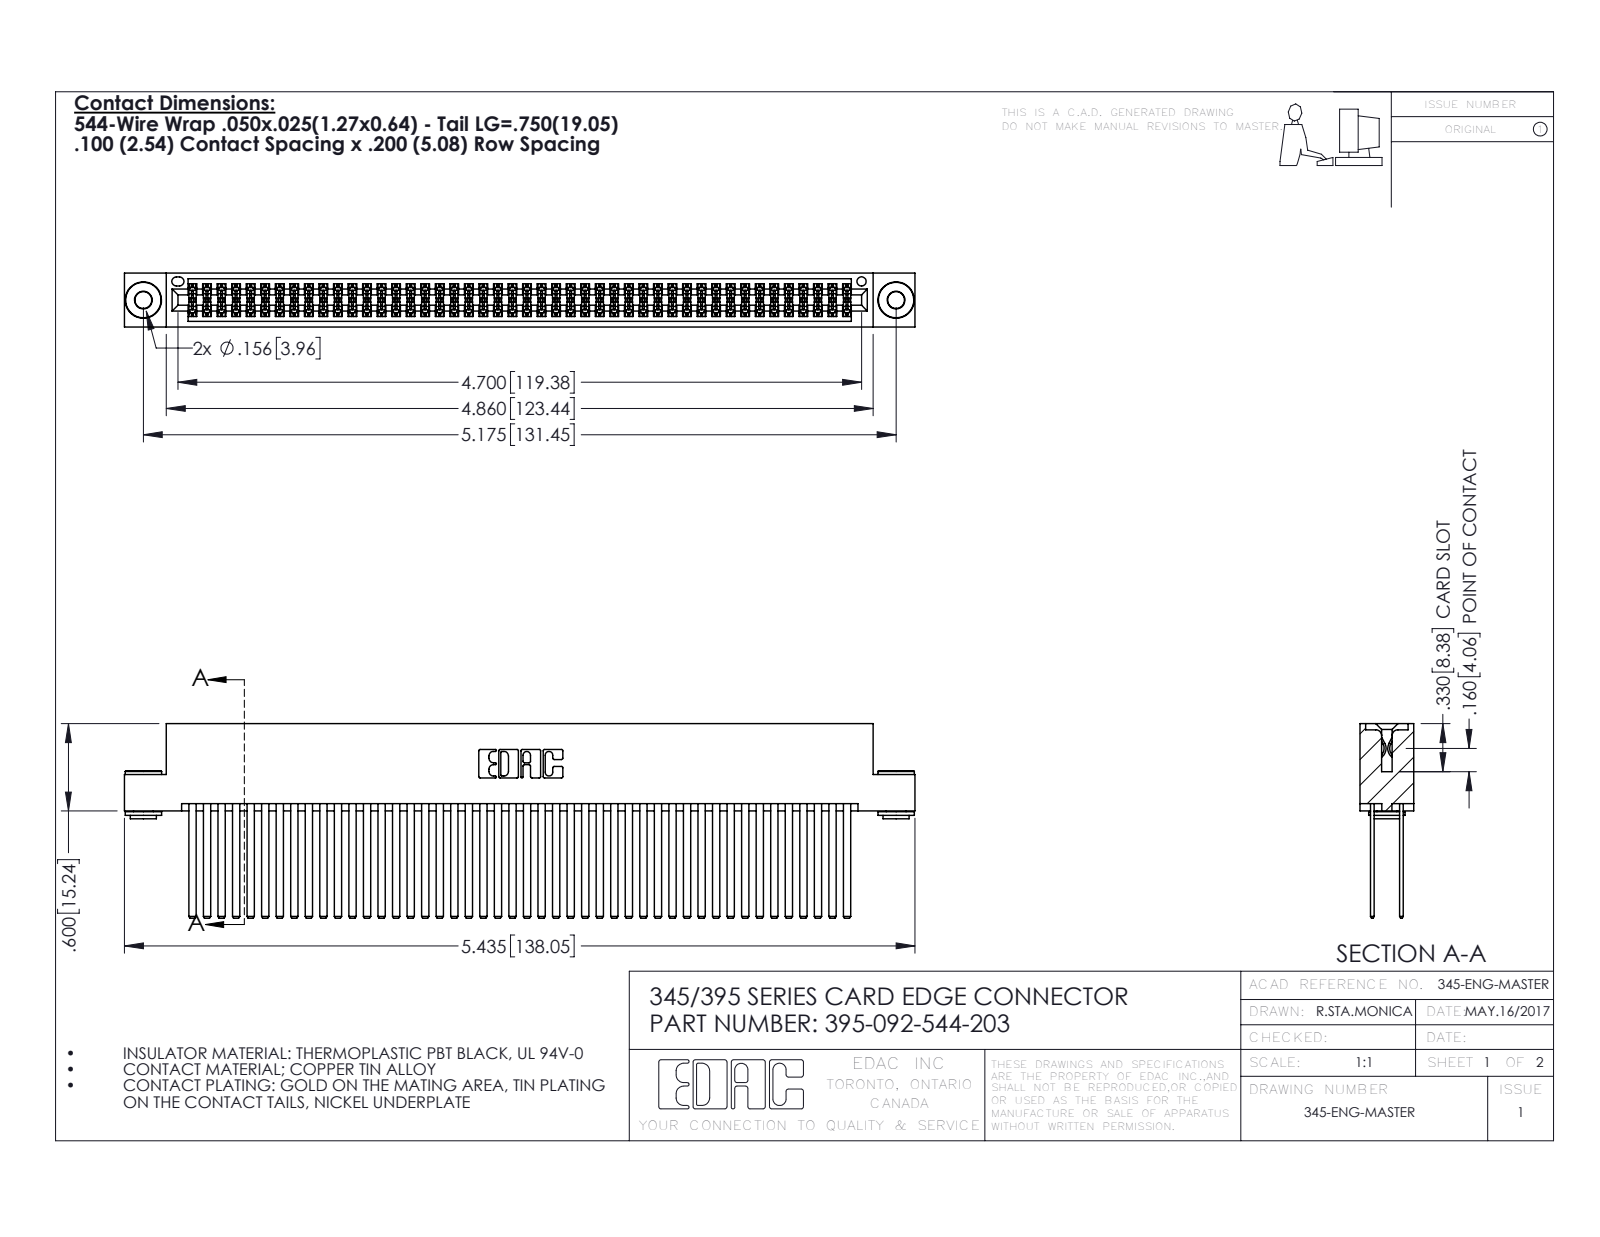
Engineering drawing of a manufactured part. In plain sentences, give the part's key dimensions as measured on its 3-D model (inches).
The part is named "345-292-001_345-293-144; 345 Part_Flush Mounting Lugs - 0.156 Dia-TH; 345-250-002_345-250-002-102; 395-092-544-203". Its 3-D file was written by "SolidWorks 2016 (CONFIG_CONTROL_DESIGN)". It is 95 solids with 4212 faces: 2758 planar, 1446 cylindrical and 8 other. Overall it measures 5.435 by 1.337 by 0.37 inches. Its volume is 0.9 cubic inches and its surface area 40.11 square inches. Round holes: 2 of diameter 0.116, 2 of diameter 0.156, 1 of diameter 0.064. Round bosses or shafts: 2 of diameter 0.25, 2 of diameter 0.18, 2 of diameter 0.136. Partial cylindrical surfaces (rounded edges, fillets, slot ends): 138 of radius 0.006, 22 of radius 0.01, 6 of radius 0.007, 6 of radius 0.031, 3 of radius 0.026, 2 of radius 0.014, 2 of radius 0.019, 2 of radius 0.022. The main face-to-face distances are 0.2, 0.025, 0.072, 0.098, 0.272, 0.298, 0.225, 0.175, 0.37, 0.05. The hole center spacings are 0.27, 4.939, 5.175.
